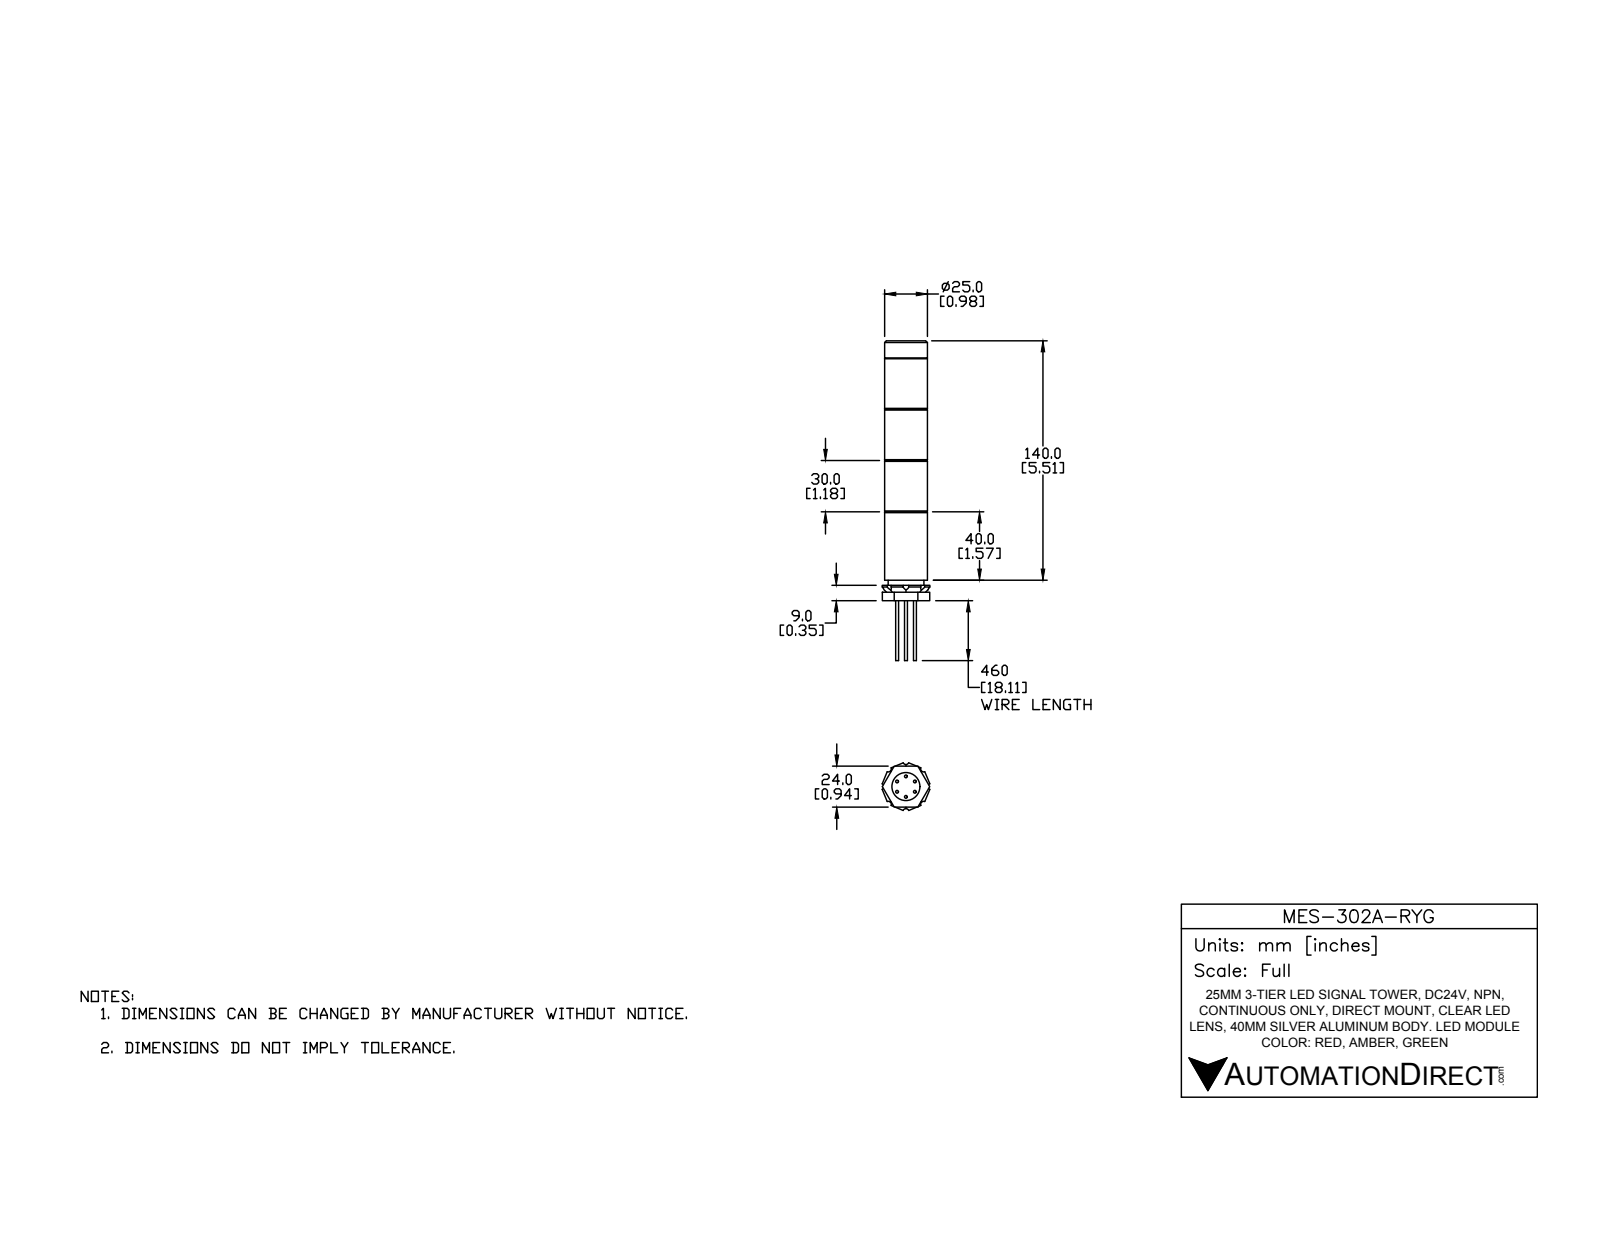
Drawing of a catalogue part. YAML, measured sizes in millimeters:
part_name: "MES-302A-RYG"
step_written_by: "SolidWorks 2016 (AUTOMOTIVE_DESIGN)"
units: millimeters
bodies: {solids: 14, faces: 148, planar: 75, cylindrical: 51, other: 22}
overall_size: [187, 27.89, 27.89]
volume: 63077
surface_area: 25272
round_holes:
  - {diameter: 3.2, count: 1}
  - {diameter: 7.7, count: 1}
  - {diameter: 16.4, count: 1}
  - {diameter: 18, count: 1}
  - {diameter: 20.7, count: 1}
  - {diameter: 21, count: 1}
round_bosses_or_shafts:
  - {diameter: 1.7, count: 6}
  - {diameter: 25, count: 1}
  - {diameter: 20.9, count: 1}
  - {diameter: 16, count: 1}
  - {diameter: 5, count: 1}
partial_cylinders:
  - {radius: 1.75, count: 8}
face_to_face_distances: [30, 60, 90, 40, 7, 107, 70, 100, 37, 67]
